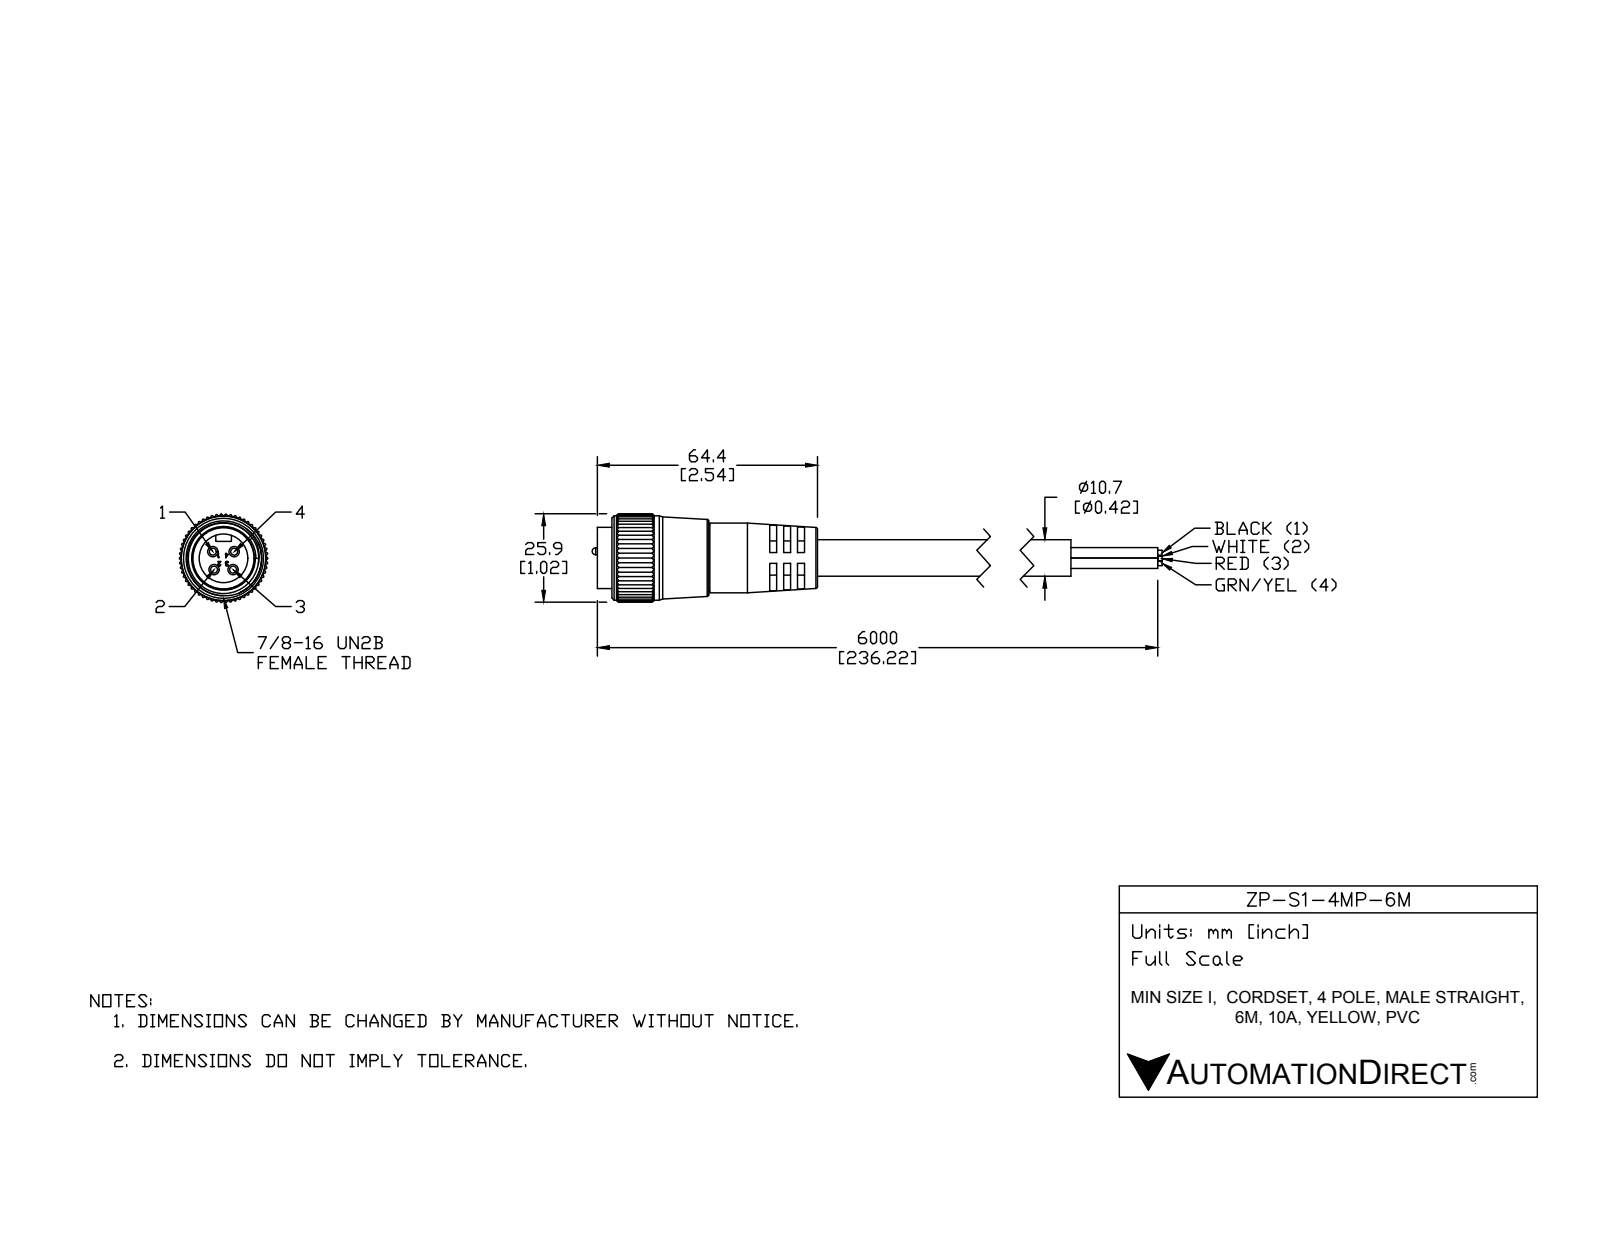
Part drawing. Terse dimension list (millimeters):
name: ZP-S1-4MP-6M
written by: SolidWorks 2015 (AUTOMOTIVE_DESIGN)
unit: mm
bodies: 6 solids, 589 faces (213 planar, 318 cylindrical, 58 other)
size: 110 × 52.91 × 25.84
volume: 27 918 mm³; area: 12 834 mm²
holes: 1× ⌀14.22, 1× ⌀19.96, 1× ⌀20.45, 1× ⌀21
bosses: 4× ⌀3.05, 4× ⌀2, 2× ⌀10.67, 1× ⌀24.68, 1× ⌀20.4, 1× ⌀19.5, 1× ⌀17.88
rounds: 165× R0.25, 1× R2.29, 1× R5.25, 1× R12.93
face distances: 2, 4.04, 2.04, 6.04, 13.88, 11.88, 9.84, 7.84, 5.82, 8.06
